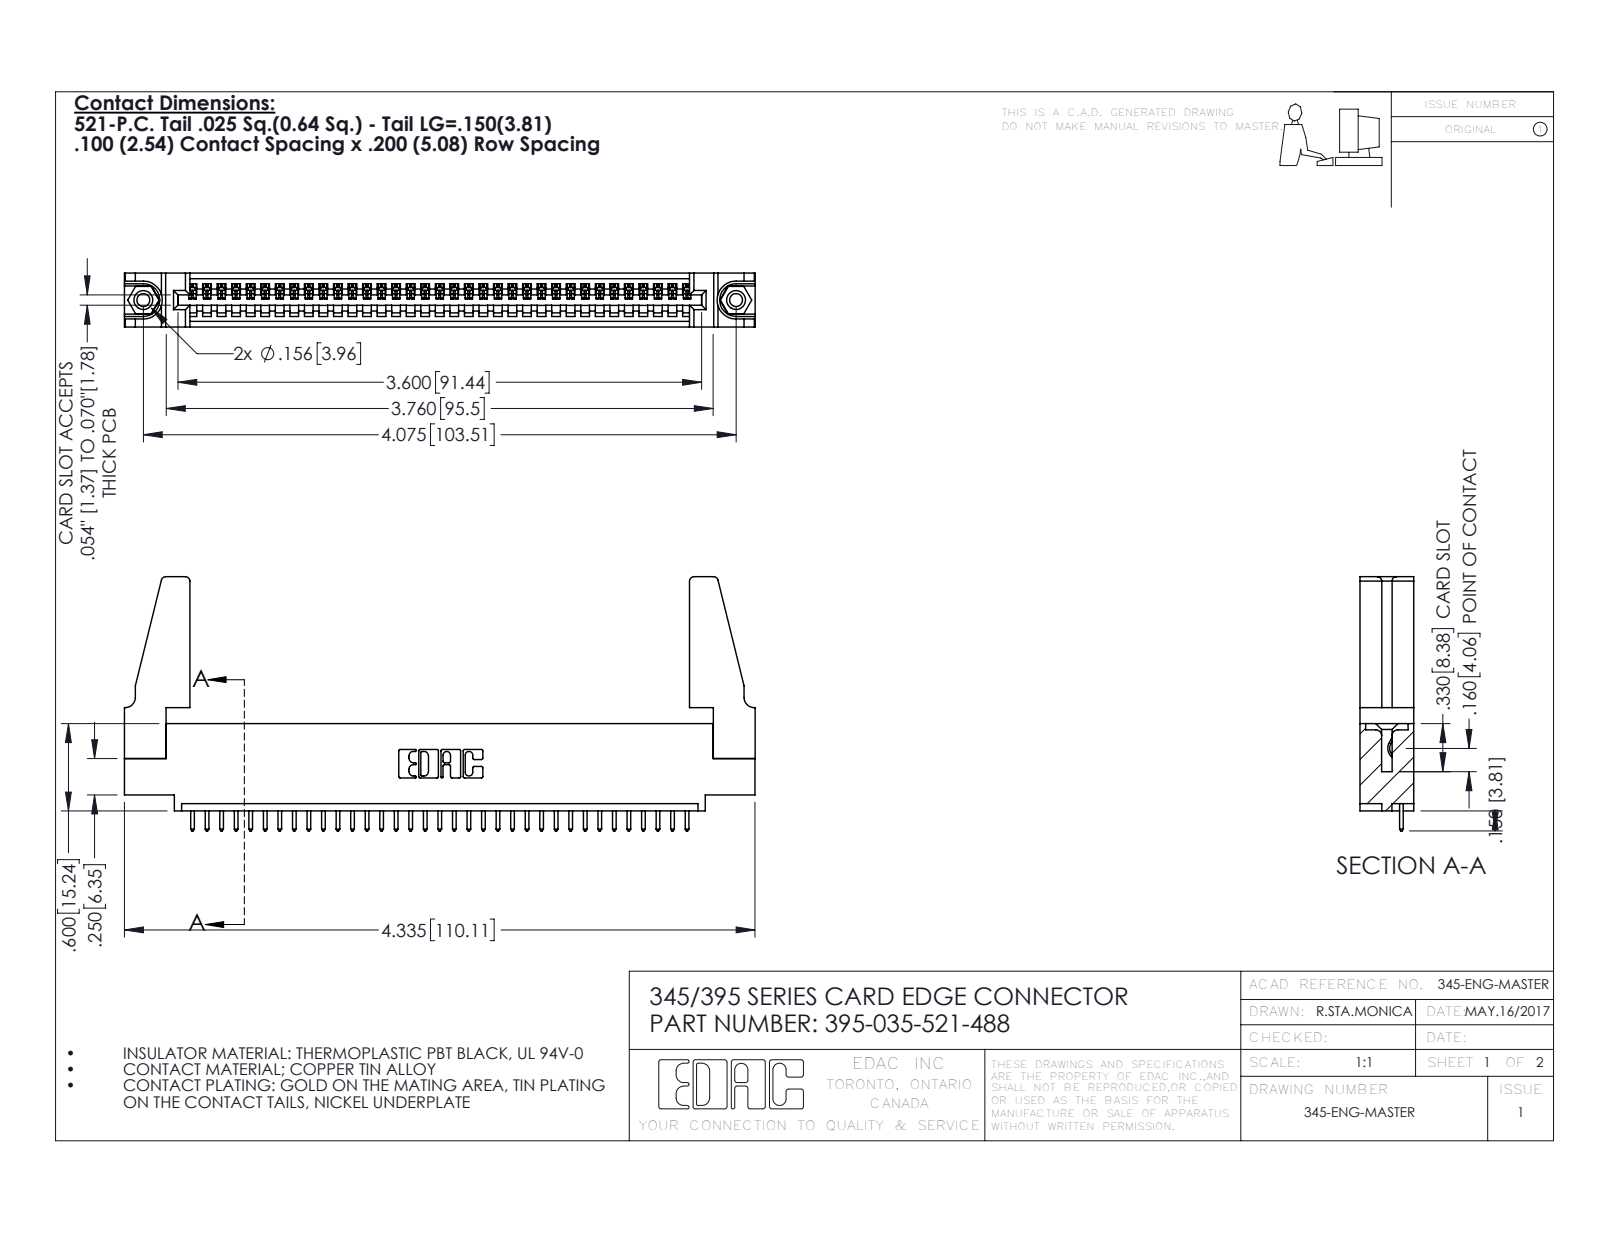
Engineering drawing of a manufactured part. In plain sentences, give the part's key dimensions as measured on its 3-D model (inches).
The part is named "345-220-078_345-220-088; 345-292-001_345-293-121; 345-250-001_345-250-001-102; 395-035-521-488 (+1 more)". Its 3-D file was written by "SolidWorks 2016 (CONFIG_CONTROL_DESIGN)". It is 40 solids with 2284 faces: 1556 planar, 712 cylindrical and 16 other. Overall it measures 4.336 by 1.747 by 0.37 inches. Its volume is 0.823 cubic inches and its surface area 25.3 square inches. Round holes: 2 of diameter 0.089, 2 of diameter 0.125, 2 of diameter 0.156, 1 of diameter 0.064. Round bosses or shafts: 2 of diameter 0.155. Partial cylindrical surfaces (rounded edges, fillets, slot ends): 70 of radius 0.006, 70 of radius 0.01, 22 of radius 0.01, 8 of radius 0.03, 6 of radius 0.007, 6 of radius 0.031, 3 of radius 0.026, 2 of radius 0.031. The main face-to-face distances are 0.072, 0.37, 0.298, 0.2, 0.098, 0.272, 0.025, 0.225, 0.149, 0.072. The hole center spacings are 0.27, 3.839, 4.075.
